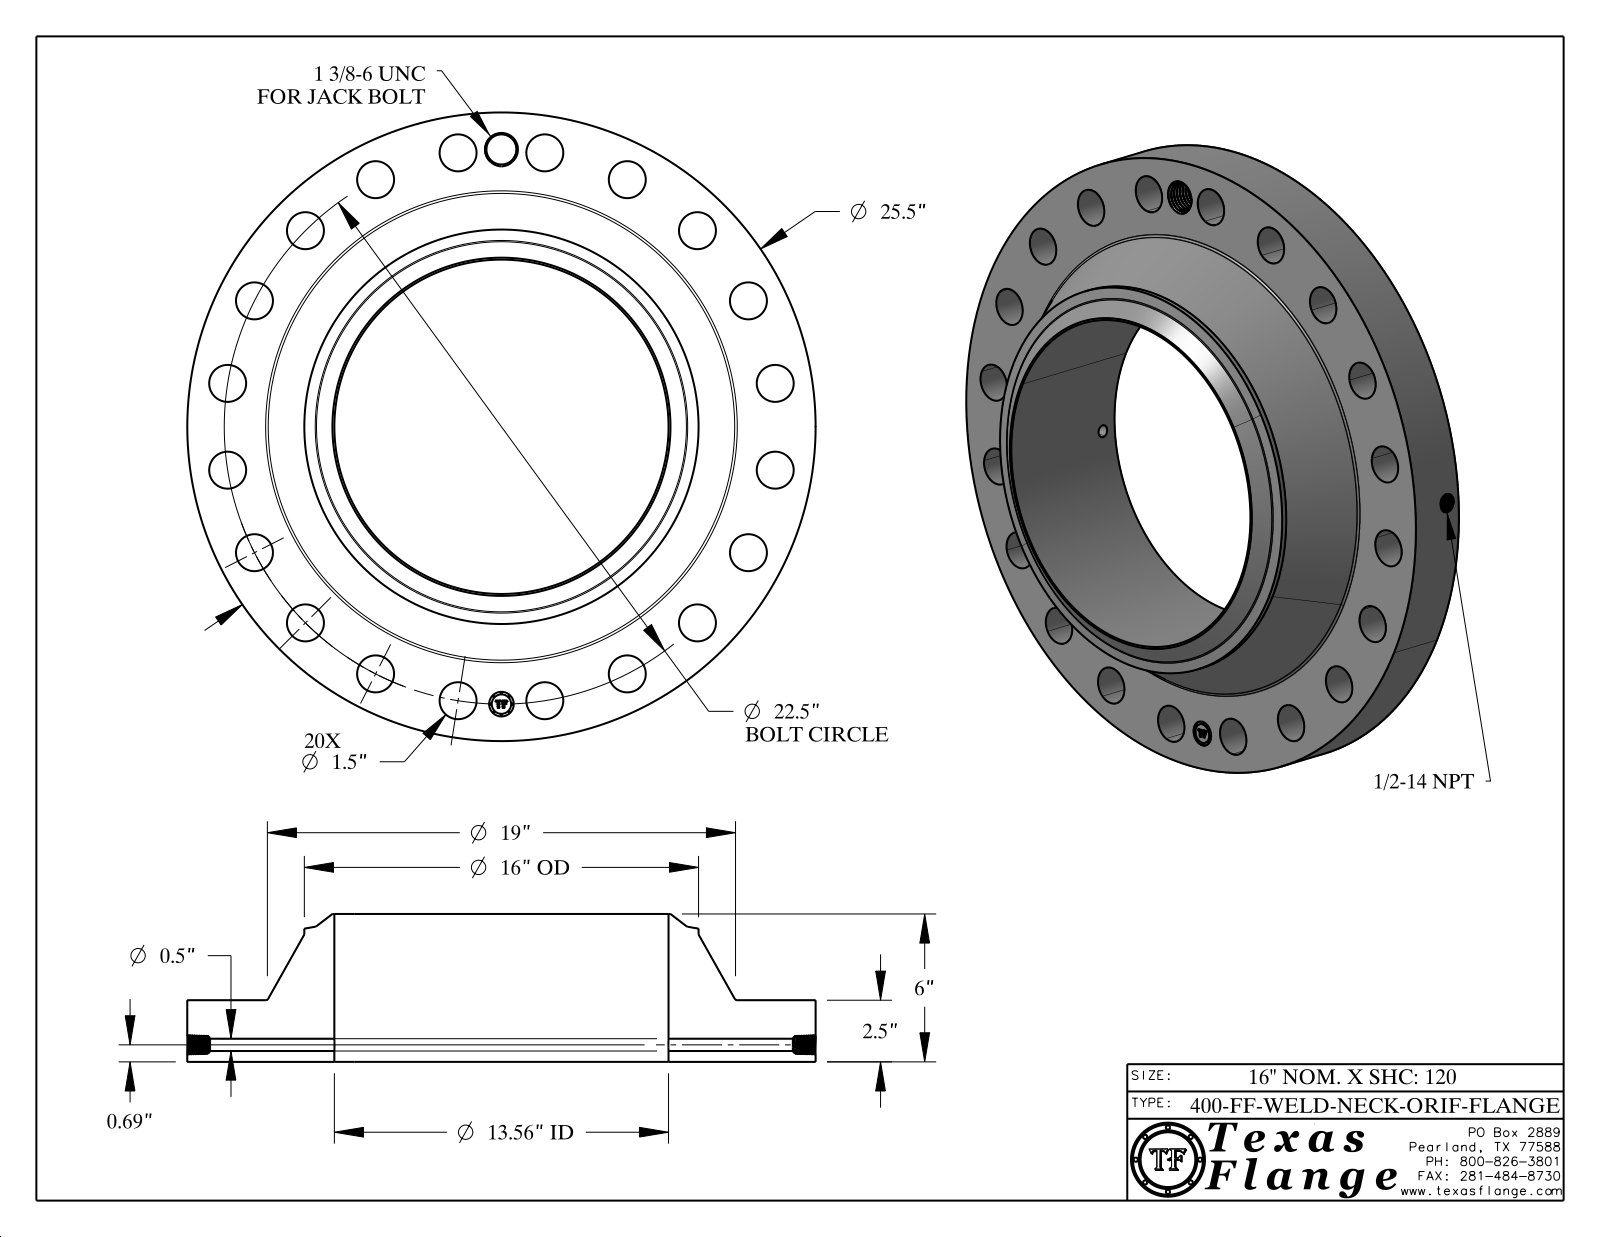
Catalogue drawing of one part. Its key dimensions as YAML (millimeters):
part_name: "400-FF-WELD-NECK"
step_written_by: "CATIA V5 STEP AP214 (AUTOMOTIVE_DESIGN)"
units: millimeters
bodies: {solids: 1, faces: 794, planar: 368, cylindrical: 116, other: 310}
overall_size: [647.7, 647.7, 152.4]
volume: 18120000
surface_area: 962600
round_holes:
  - {diameter: 38.1, count: 20}
  - {diameter: 12.7, count: 1}
  - {diameter: 17.1, count: 1}
  - {diameter: 25.4, count: 1}
  - {diameter: 31, count: 1}
  - {diameter: 344.5, count: 1}
round_bosses_or_shafts:
  - {diameter: 1.5, count: 8}
  - {diameter: 647.7, count: 1}
  - {diameter: 406.4, count: 1}
  - {diameter: 20, count: 1}
face_to_face_distances: [63.5, 152.4, 88.9, 63.1, 0.4, 89.3, 7.6, 7.4, 1.4, 6.3]
hole_center_spacings: [89.4, 259.5, 462.4, 509.2, 543.5, 176.6, 285.8, 335.9]
